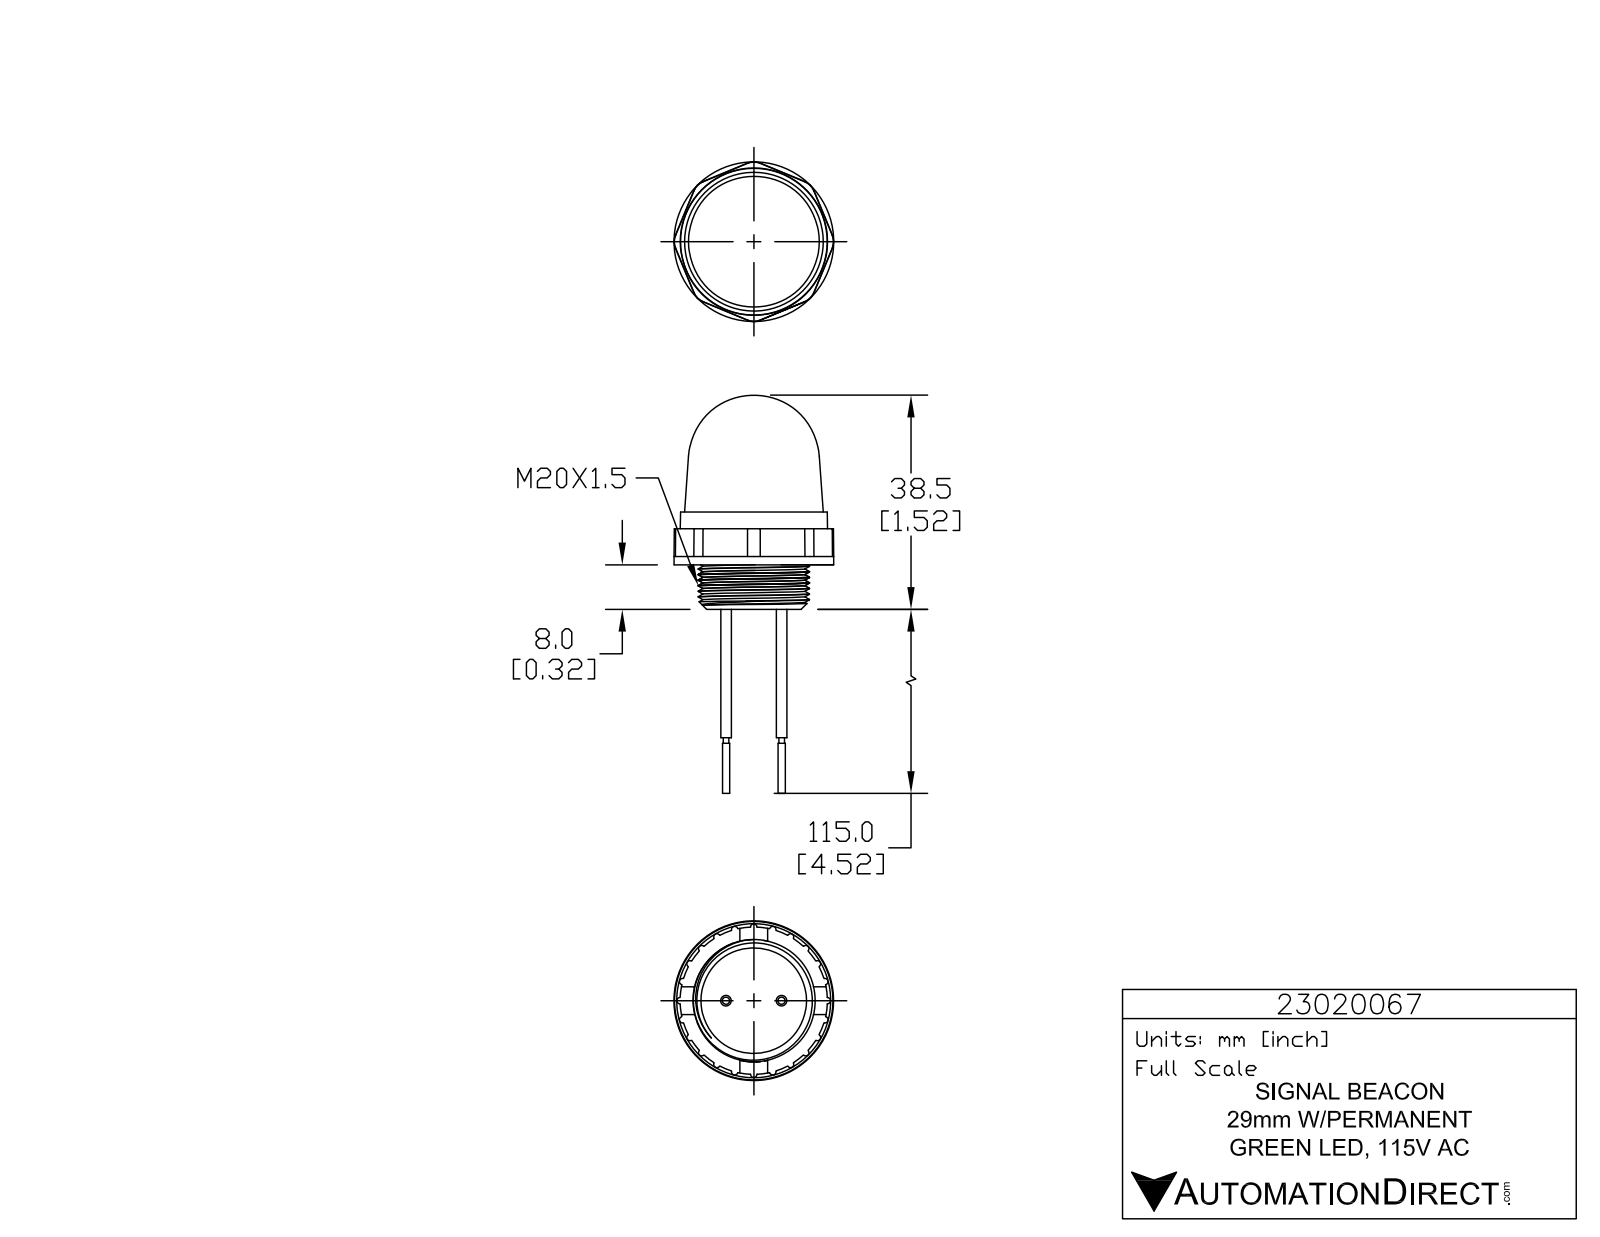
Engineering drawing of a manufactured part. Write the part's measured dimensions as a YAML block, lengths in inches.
part_name: "23020067"
step_written_by: "SolidWorks 2017 (AUTOMOTIVE_DESIGN)"
units: inches
bodies: {solids: 1, faces: 844, planar: 551, cylindrical: 203, other: 90}
overall_size: [2.82, 1.131, 1.131]
volume: 0.978
surface_area: 8.158
round_holes:
  - {diameter: 0.02, count: 3}
  - {diameter: 0.807, count: 1}
round_bosses_or_shafts:
  - {diameter: 0.113, count: 3}
  - {diameter: 0.028, count: 3}
  - {diameter: 0.075, count: 2}
  - {diameter: 0.051, count: 2}
  - {diameter: 0.039, count: 2}
  - {diameter: 1.131, count: 1}
  - {diameter: 1.122, count: 1}
  - {diameter: 0.894, count: 1}
partial_cylinders:
  - {radius: 0.118, count: 8}
  - {radius: 0.004, count: 6}
  - {radius: 0.004, count: 6}
  - {radius: 0.004, count: 6}
  - {radius: 0.065, count: 6}
  - {radius: 0.005, count: 3}
  - {radius: 0.007, count: 3}
  - {radius: 0.008, count: 3}
face_to_face_distances: [0.276, 0.374, 0.039, 0.315, 0.65, 0.638, 0.362, 0.689, 0.413, 0.051]
